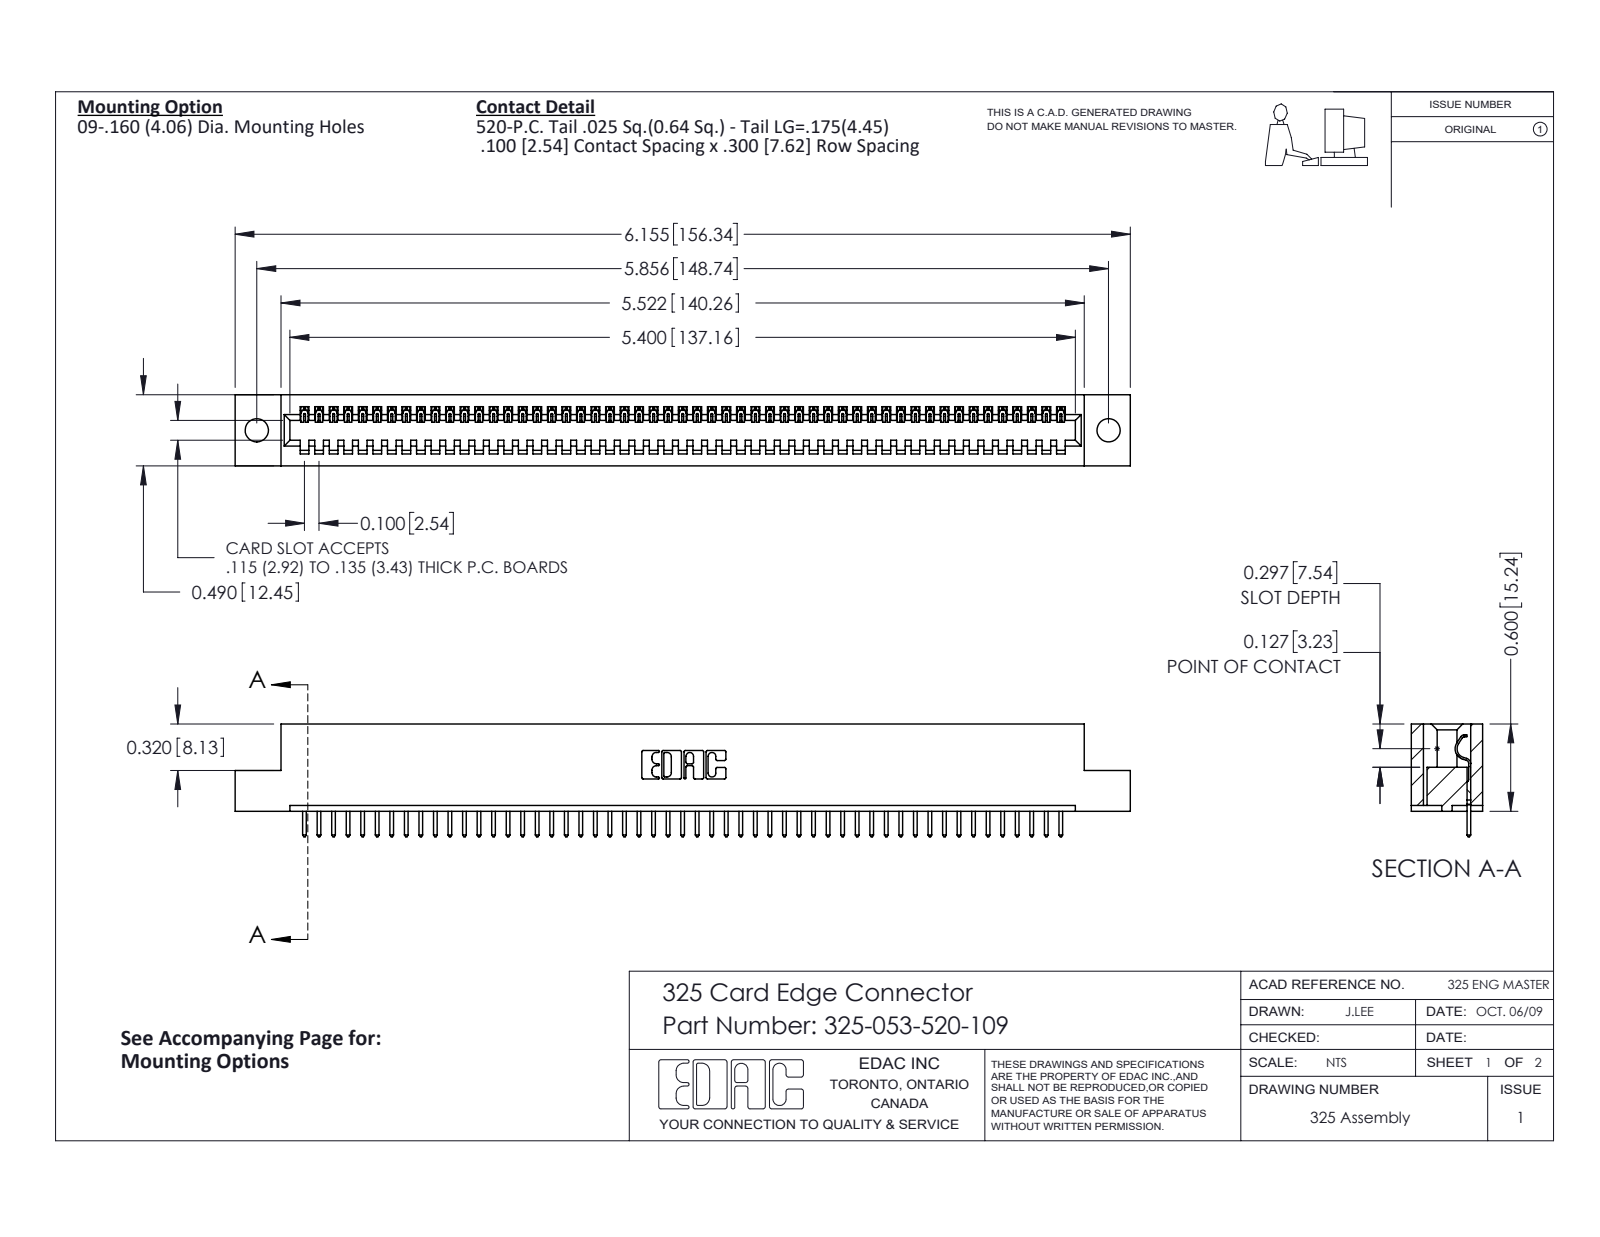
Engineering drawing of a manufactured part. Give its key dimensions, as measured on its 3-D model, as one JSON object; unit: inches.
{"part_name": "325-053-520-109; 325-292-001_325-293-120; 325 Part_.160 TH", "step_written_by": "SolidWorks 2016 (CONFIG_CONTROL_DESIGN)", "units": "inches", "bodies": {"solids": 54, "faces": 3188, "planar": 2296, "cylindrical": 892, "other": 0}, "overall_size": [6.155, 0.775, 0.49], "volume_in3": 1.194, "surface_area_in2": 32.4, "round_holes": [[0.16, 2]], "partial_cylinders_radius": [[0.006, 106], [0.01, 106], [0.01, 22], [0.007, 6], [0.031, 6], [0.026, 3], [0.014, 1], [0.022, 1]], "face_to_face_distances": [0.083, 0.407, 0.49, 0.3, 0.107, 0.383, 0.025, 0.325, 0.263, 0.56], "hole_center_spacings": [5.856]}
